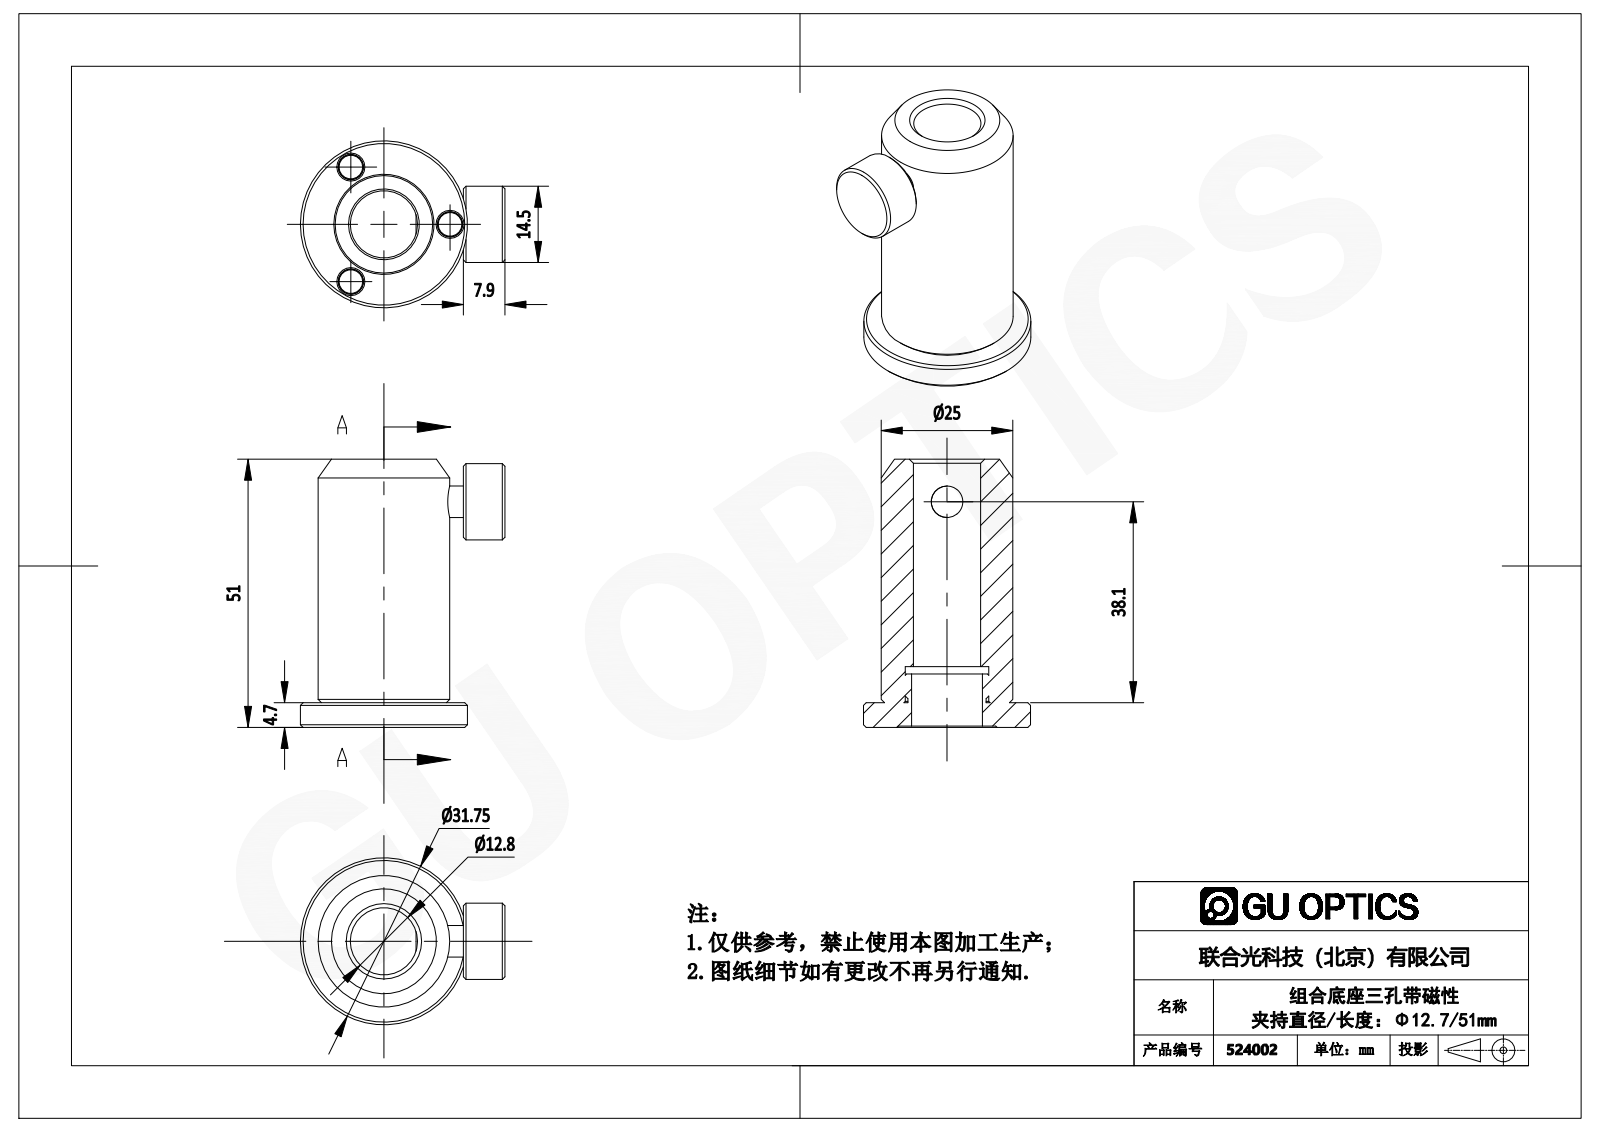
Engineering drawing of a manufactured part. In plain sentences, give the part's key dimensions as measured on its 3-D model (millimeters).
The part is named "524002". Its 3-D file was written by "SolidWorks 2016 (AUTOMOTIVE_DESIGN)". It is 5 solids with 90 faces: 19 planar, 31 cylindrical and 40 other. Overall it measures 51 by 38.88 by 31.75 millimeters. Its volume is 20 608 cubic millimeters and its surface area 9 133 square millimeters. Round holes: 3 of diameter 4.83, 1 of diameter 6, 1 of diameter 12.78, 1 of diameter 13.46, 1 of diameter 15.87. Round bosses or shafts: 3 of diameter 4.76, 1 of diameter 31.75, 1 of diameter 25.01, 1 of diameter 14.86, 1 of diameter 14.5. Partial cylindrical surfaces (rounded edges, fillets, slot ends): 1 of radius 7.94. The main face-to-face distances are 4.7, 51, 46.3, 4.44, 50.74, 7.9, 11.56, 11.3, 6.86, 39.44. The hole center spacings are 21.78, 12.58, 12.57.
